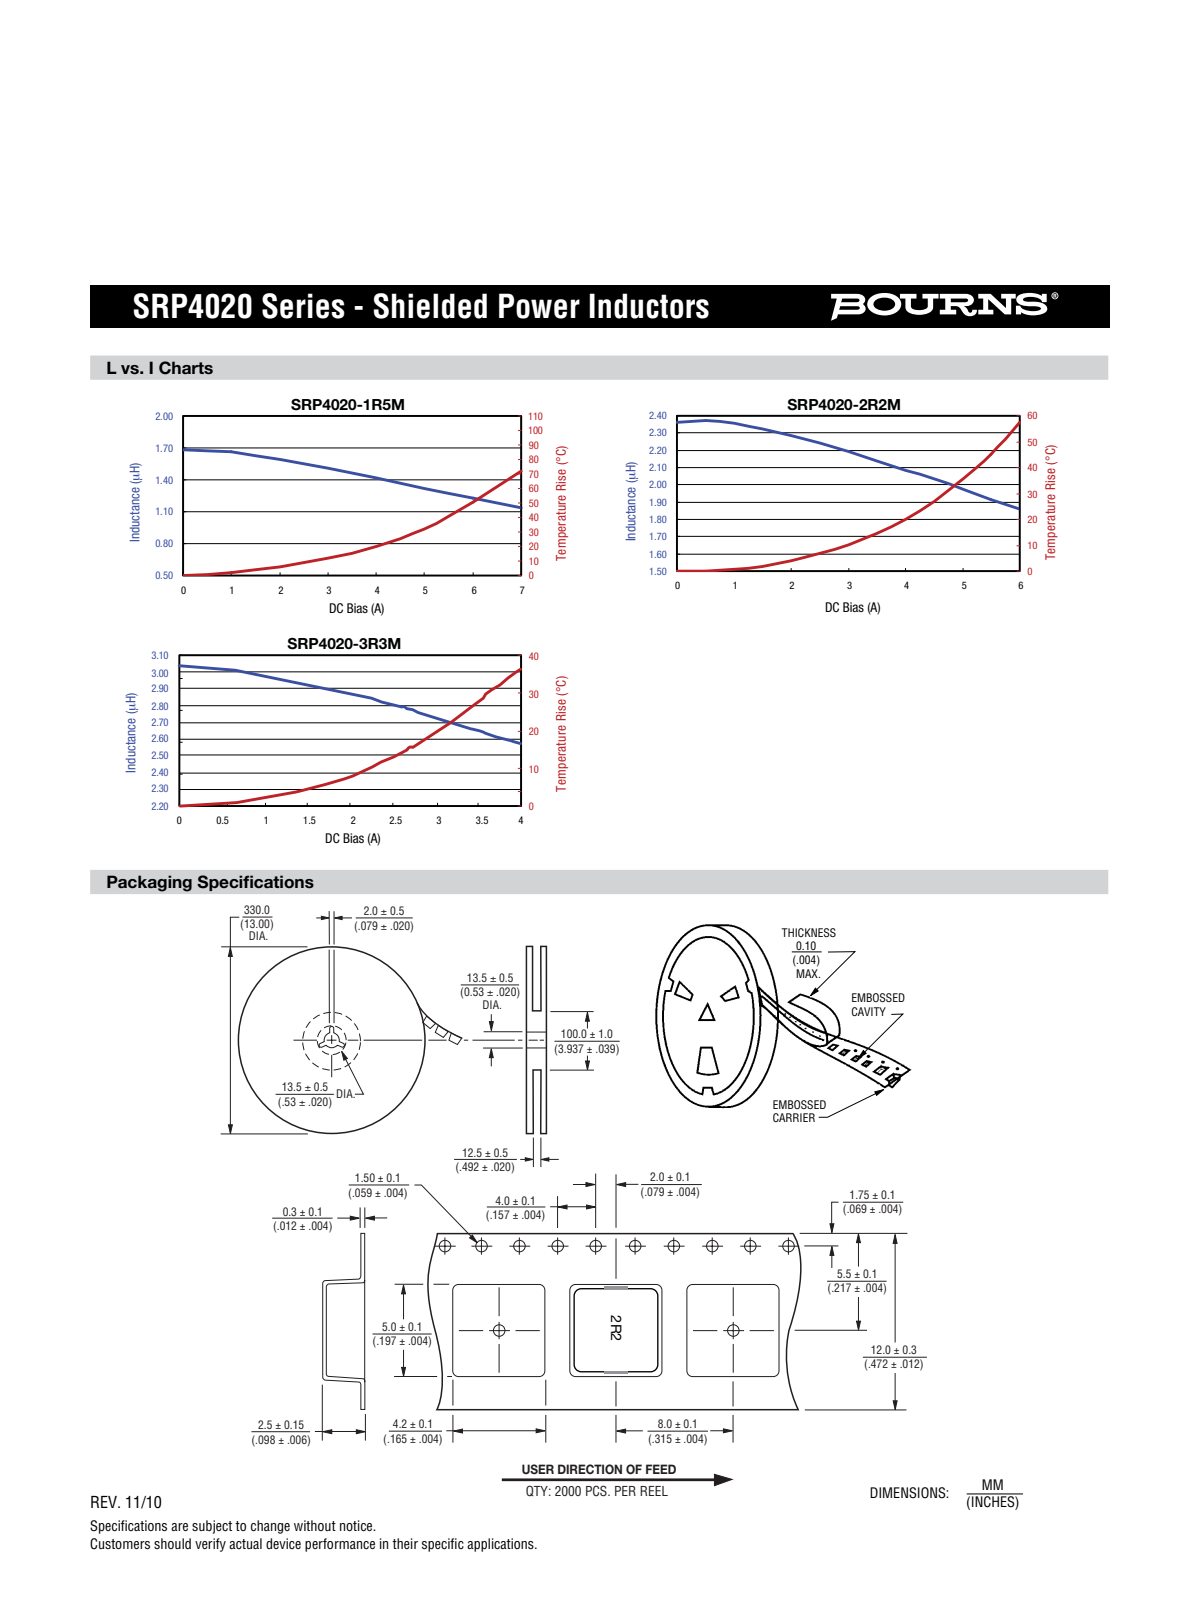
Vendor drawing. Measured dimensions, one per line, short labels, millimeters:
name: SRP4020
written by: PRO/ENGINEER BY PARAMETRIC TECHNOLOGY CORPORATION, 2010100 (CONFIG_CONTROL_DESIGN)
unit: mm
bodies: 1 solid, 24 faces (18 planar, 6 cylindrical, 0 other)
size: 4.8 × 4 × 2
volume: 28 mm³; area: 61 mm²
rounds: 4× R0.3, 2× R0.2
face distances: 1.7, 4, 2.3, 0.4, 0.6, 0.8, 2, 4.4, 0.5, 1.2
